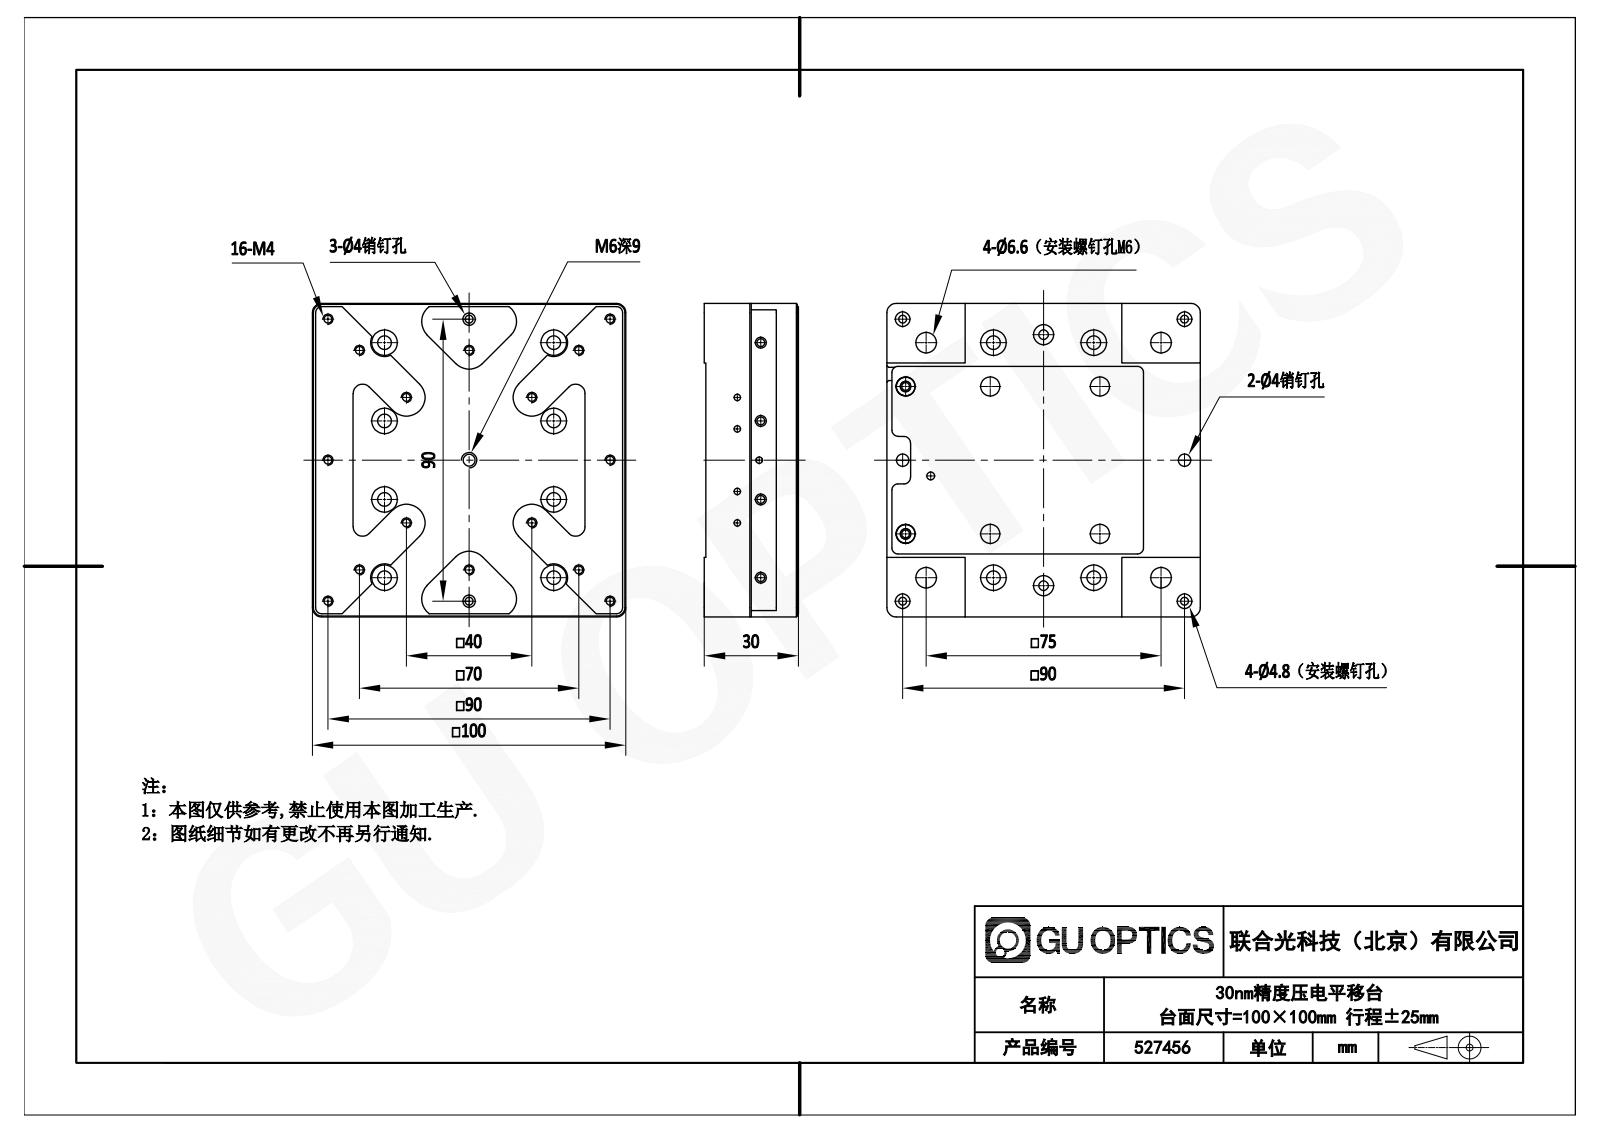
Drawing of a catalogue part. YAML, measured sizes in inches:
part_name: "527456"
step_written_by: "SolidWorks 2020 (CONFIG_CONTROL_DESIGN)"
units: inches
bodies: {solids: 3, faces: 551, planar: 286, cylindrical: 214, other: 51}
overall_size: [3.937, 3.937, 1.181]
volume: 15.78
surface_area: 121.3
round_holes:
  - {diameter: 0.098, count: 19}
  - {diameter: 0.177, count: 18}
  - {diameter: 0.13, count: 16}
  - {diameter: 0.325, count: 16}
  - {diameter: 0.134, count: 6}
  - {diameter: 0.244, count: 6}
  - {diameter: 0.081, count: 5}
  - {diameter: 0.138, count: 4}
  - {diameter: 0.157, count: 4}
  - {diameter: 0.189, count: 4}
  - {diameter: 0.26, count: 4}
  - {diameter: 0.441, count: 4}
partial_cylinders:
  - {radius: 0.098, count: 34}
  - {radius: 0.079, count: 20}
  - {radius: 0.118, count: 13}
  - {radius: 0.236, count: 10}
  - {radius: 0.075, count: 6}
  - {radius: 0.177, count: 4}
  - {radius: 0.02, count: 2}
  - {radius: 0.059, count: 2}
face_to_face_distances: [0.02, 0.354, 0.335, 0.244, 0.906, 0.551, 0.598, 0.256, 0.925, 0.571]
hole_center_spacings: [0.984, 2.953, 0.637, 1.261, 1.48, 1.506, 1.772, 2.366]
